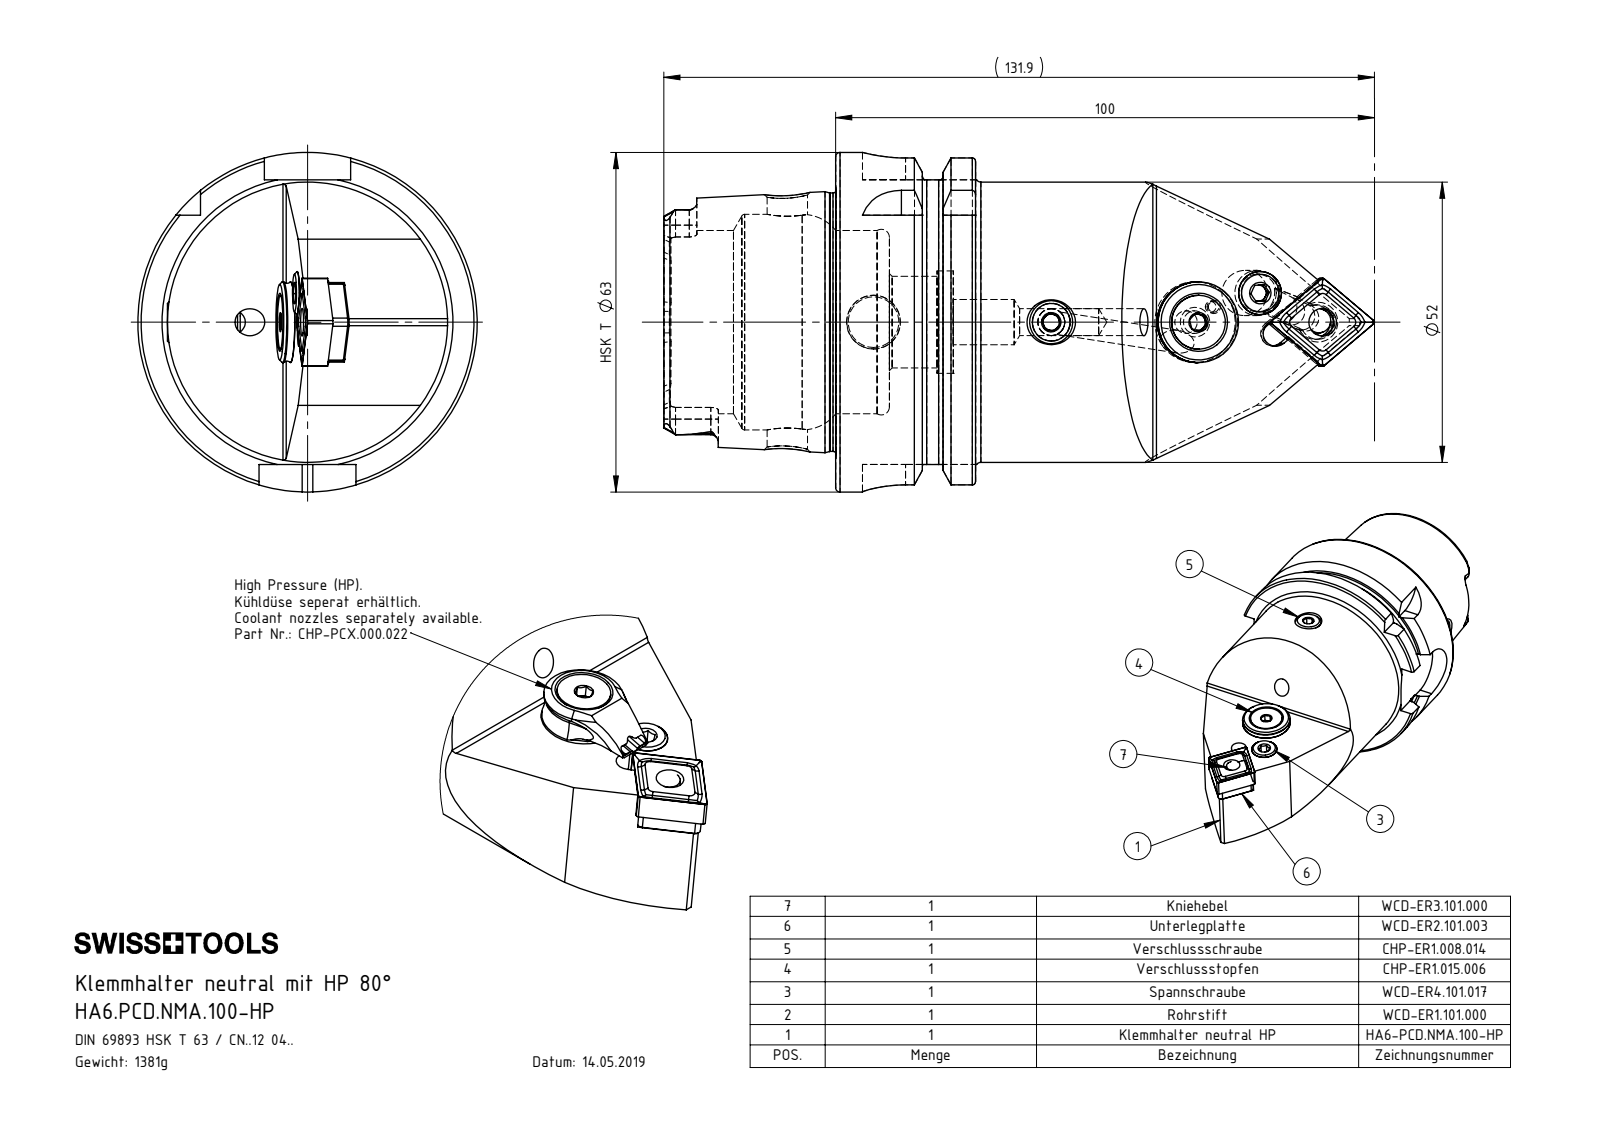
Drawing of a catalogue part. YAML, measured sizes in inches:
part_name: "WCD-ER1.101.000; DIN 3771 - 13x1; CNMG120408; HA6-PCD.NMA.100-HP_F (+8 more)"
step_written_by: "SolidWorks 2022 (AUTOMOTIVE_DESIGN)"
units: inches
bodies: {solids: 11, faces: 496, planar: 160, cylindrical: 137, other: 199}
overall_size: [5.184, 2.48, 2.48]
volume: 10.67
surface_area: 57.73
round_holes:
  - {diameter: 0.197, count: 3}
  - {diameter: 0.165, count: 2}
  - {diameter: 0.276, count: 2}
  - {diameter: 0.331, count: 2}
  - {diameter: 0.047, count: 1}
  - {diameter: 0.079, count: 1}
  - {diameter: 0.098, count: 1}
  - {diameter: 0.118, count: 1}
  - {diameter: 0.203, count: 1}
  - {diameter: 0.205, count: 1}
  - {diameter: 0.258, count: 1}
  - {diameter: 0.295, count: 1}
round_bosses_or_shafts:
  - {diameter: 0.315, count: 2}
  - {diameter: 2.48, count: 1}
  - {diameter: 2.163, count: 1}
  - {diameter: 2.047, count: 1}
  - {diameter: 1.887, count: 1}
  - {diameter: 0.591, count: 1}
  - {diameter: 0.528, count: 1}
  - {diameter: 0.394, count: 1}
partial_cylinders:
  - {radius: 0.055, count: 6}
  - {radius: 0.031, count: 5}
  - {radius: 0.039, count: 4}
  - {radius: 0.113, count: 4}
  - {radius: 0.315, count: 4}
  - {radius: 0.098, count: 3}
  - {radius: 0.126, count: 2}
  - {radius: 0.083, count: 1}
face_to_face_distances: [1.022, 0.63, 0.392, 1.256, 1.648, 2.278, 2.079, 0.858, 0.467, 0.177]
hole_center_spacings: [0.177, 0.178, 0.178, 0.178, 0.44, 0.44, 0.506, 0.509]
